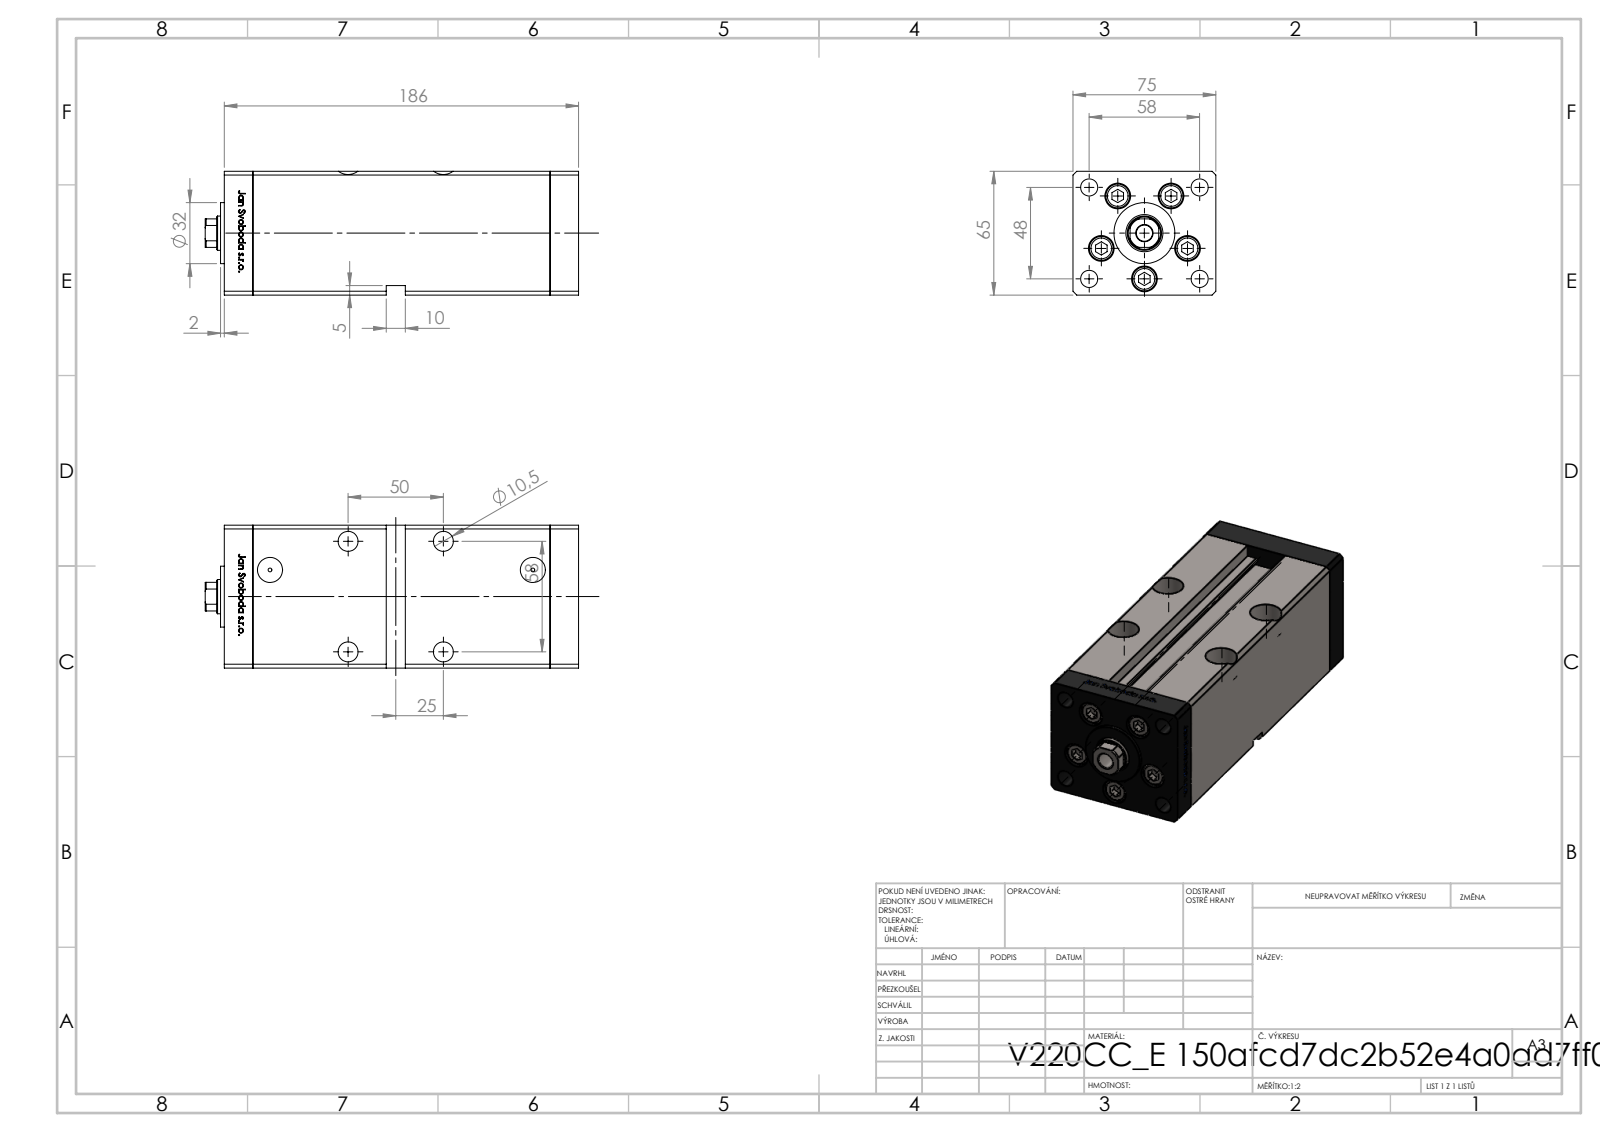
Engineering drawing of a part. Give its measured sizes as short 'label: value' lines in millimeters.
name: V220C_FRONT_E; ALLEN BOLT; V220C_VC_E; V220C BACK_E (+1 more)
written by: SolidWorks 2019 (CONFIG_CONTROL_DESIGN)
unit: mm
bodies: 14 solids, 1212 faces (473 planar, 165 cylindrical, 574 other)
size: 196 × 75 × 65
volume: 769 603 mm³; area: 146 638 mm²
holes: 9× ⌀9, 5× ⌀13.5, 4× ⌀10.5, 4× ⌀16.5, 2× ⌀2, 2× ⌀13.16, 1× ⌀8.5, 1× ⌀18, 1× ⌀19.5
bosses: 5× ⌀12.5, 5× ⌀8, 1× ⌀32
rounds: 2× R0.93, 1× R8.5
face distances: 75, 65, 15, 156, 171, 186, 28, 54.5, 10.5, 26.25
hole spacings: 24, 37.64, 58, 15.67, 17.22, 27.71, 28.83, 29
